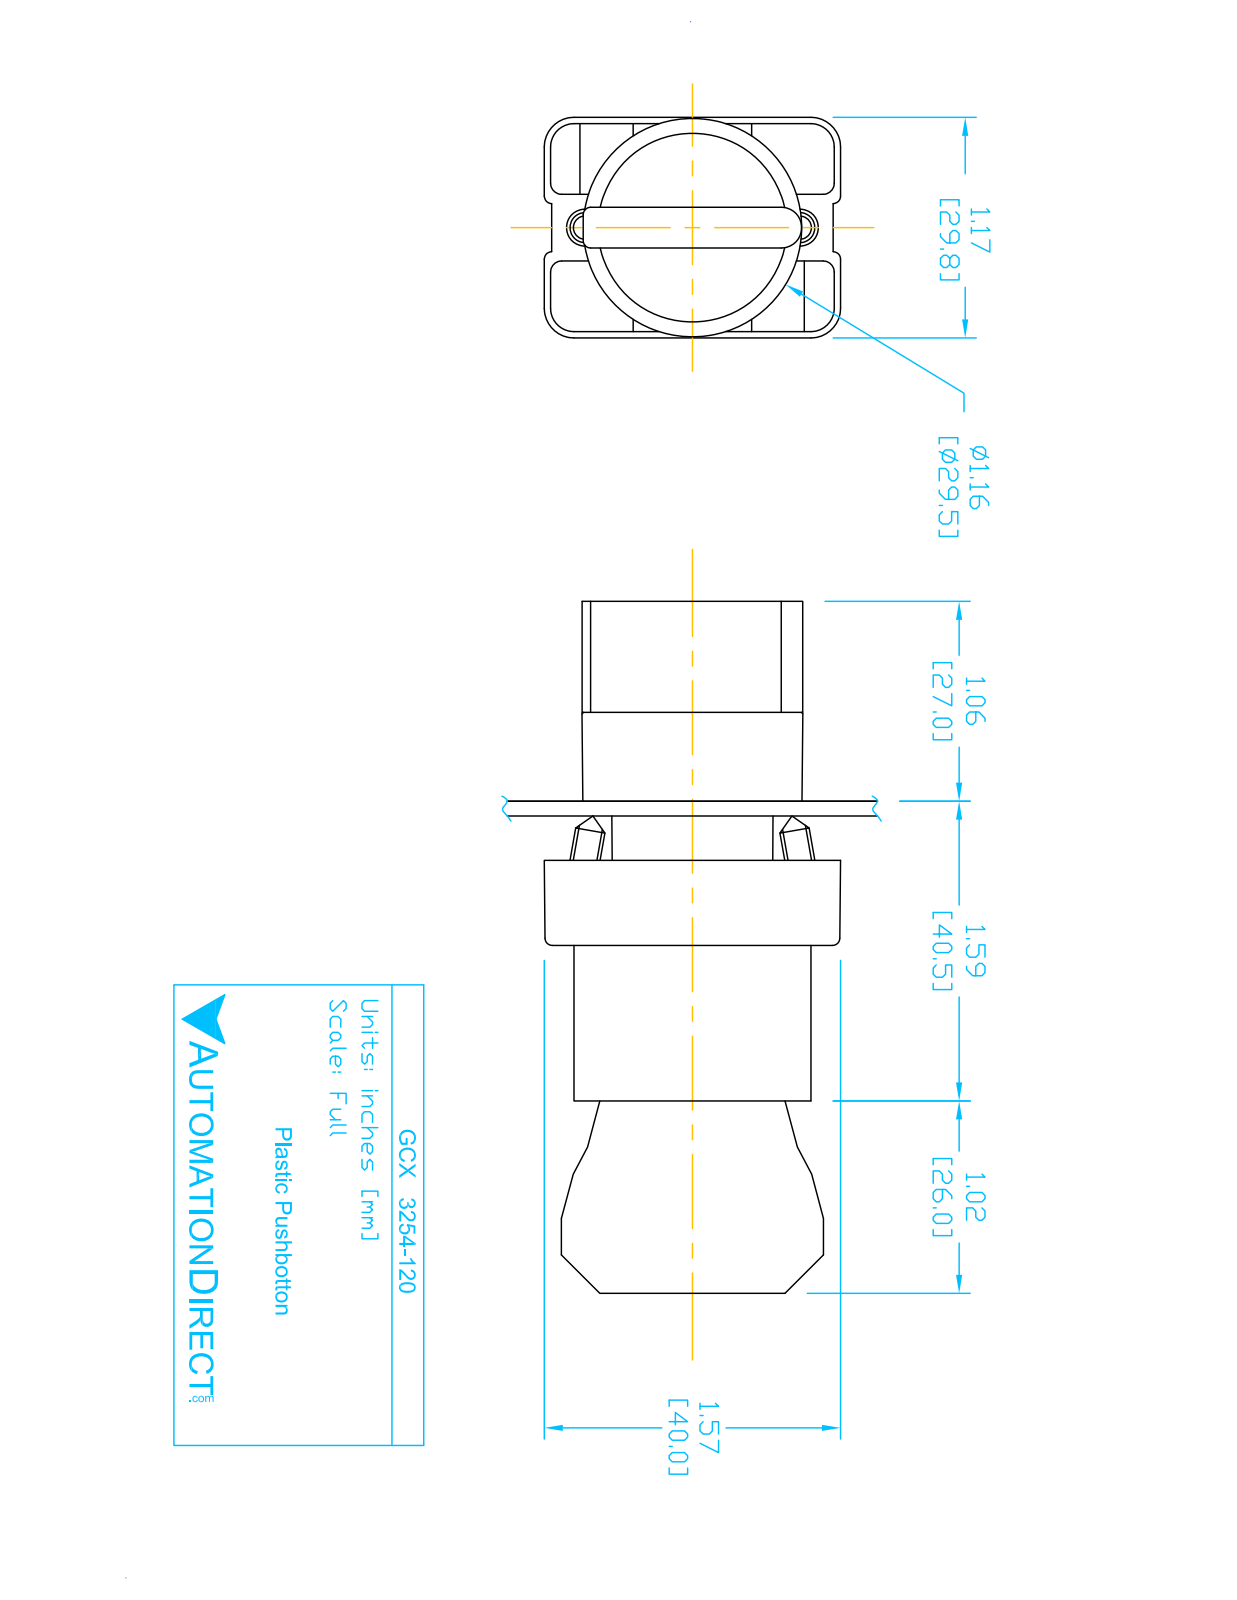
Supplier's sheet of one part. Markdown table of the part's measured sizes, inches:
| quantity | value |
| --- | --- |
| part name | ECX1050; ecx1040; GCX3254-120; ECX3029-2 (+1 more) |
| STEP written by | SolidWorks 2016 (AUTOMOTIVE_DESIGN) |
| units | inches |
| bodies | 8 solids, 445 faces (263 planar, 151 cylindrical, 31 other) |
| overall size | 3.653 × 1.581 × 1.177 |
| volume | 2.799 in³ |
| surface area | 39 in² |
| round holes (diameter × count) | 0.079 × 2, 0.124 × 2, 0.13 × 2, 0.087 × 1, 0.197 × 1, 0.469 × 1, 0.878 × 1, 0.888 × 1, 1.024 × 1 |
| round bosses / shafts (diameter × count) | 0.157 × 4, 1.175 × 1, 1.004 × 1, 0.945 × 1, 0.856 × 1, 0.78 × 1, 0.504 × 1 |
| partial cylindrical surfaces (radius × count) | 0.059 × 24, 0.041 × 12, 0.124 × 12, 0.157 × 12, 0.039 × 9, 0.128 × 2, 0.02 × 1, 0.063 × 1 |
| main face-to-face distances | 0.827, 2.02, 1.193, 0.579, 1.244, 1.171, 0.472, 0.469, 0.031, 0.033 |
| hole center spacings | 0.236, 0.544, 0.472, 0.49 |
